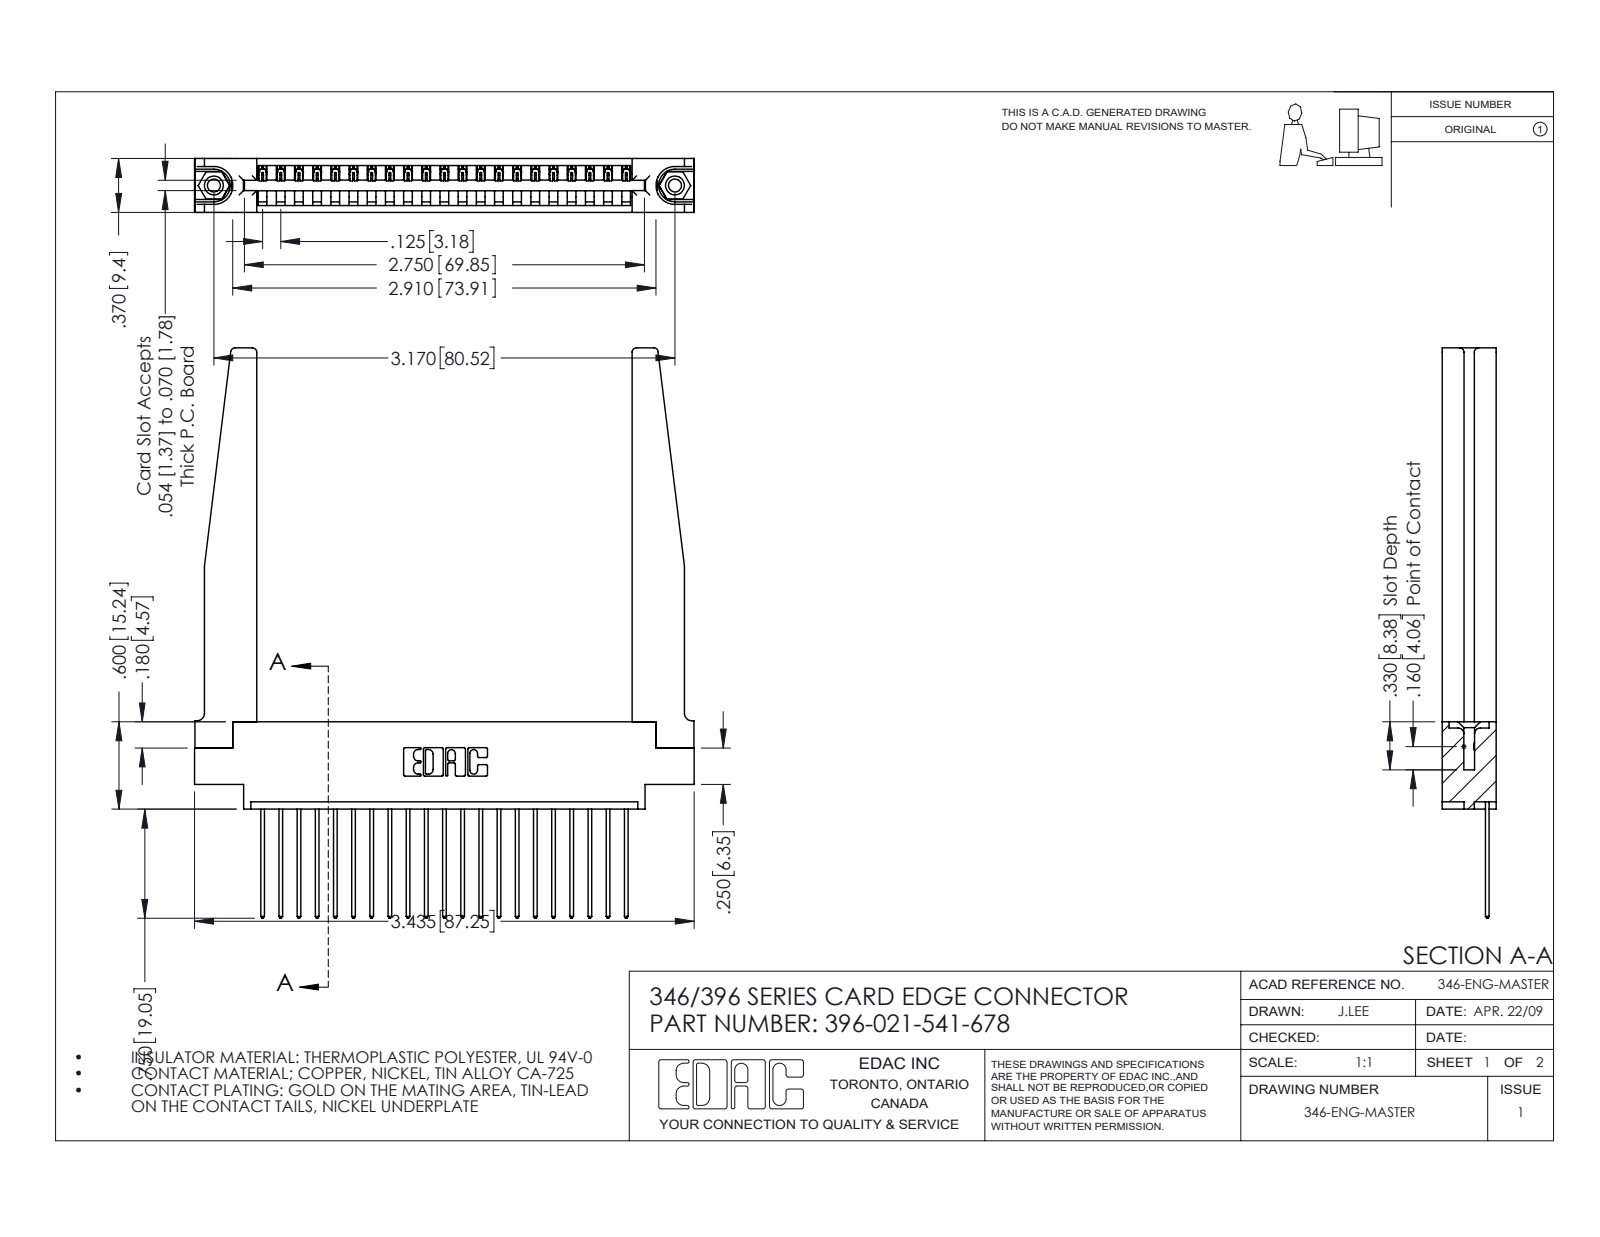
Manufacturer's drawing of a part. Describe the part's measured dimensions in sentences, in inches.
The part is named "345-292-001_345-293-141; 345-250-001_345-250-001-102; 346 Part_0.170 Offset - 0.156 Dia-TH; 396-021-541-678 (+1 more)". Its 3-D file was written by "SolidWorks 2016 (CONFIG_CONTROL_DESIGN)". It is 26 solids with 1578 faces: 1062 planar, 464 cylindrical and 52 other. Overall it measures 3.92 by 3.435 by 0.37 inches. Its volume is 0.917 cubic inches and its surface area 26.41 square inches. Round holes: 2 of diameter 0.089, 2 of diameter 0.125, 2 of diameter 0.156, 1 of diameter 0.064. Round bosses or shafts: 2 of diameter 0.155. Partial cylindrical surfaces (rounded edges, fillets, slot ends): 42 of radius 0.006, 42 of radius 0.01, 22 of radius 0.01, 8 of radius 0.03, 6 of radius 0.007, 6 of radius 0.031, 3 of radius 0.026, 2 of radius 0.031. The main face-to-face distances are 0.37, 0.072, 0.048, 0.322, 0.148, 0.15, 0.25, 0.298, 0.025, 0.222. The hole center spacings are 0.246, 2.963, 3.17.
